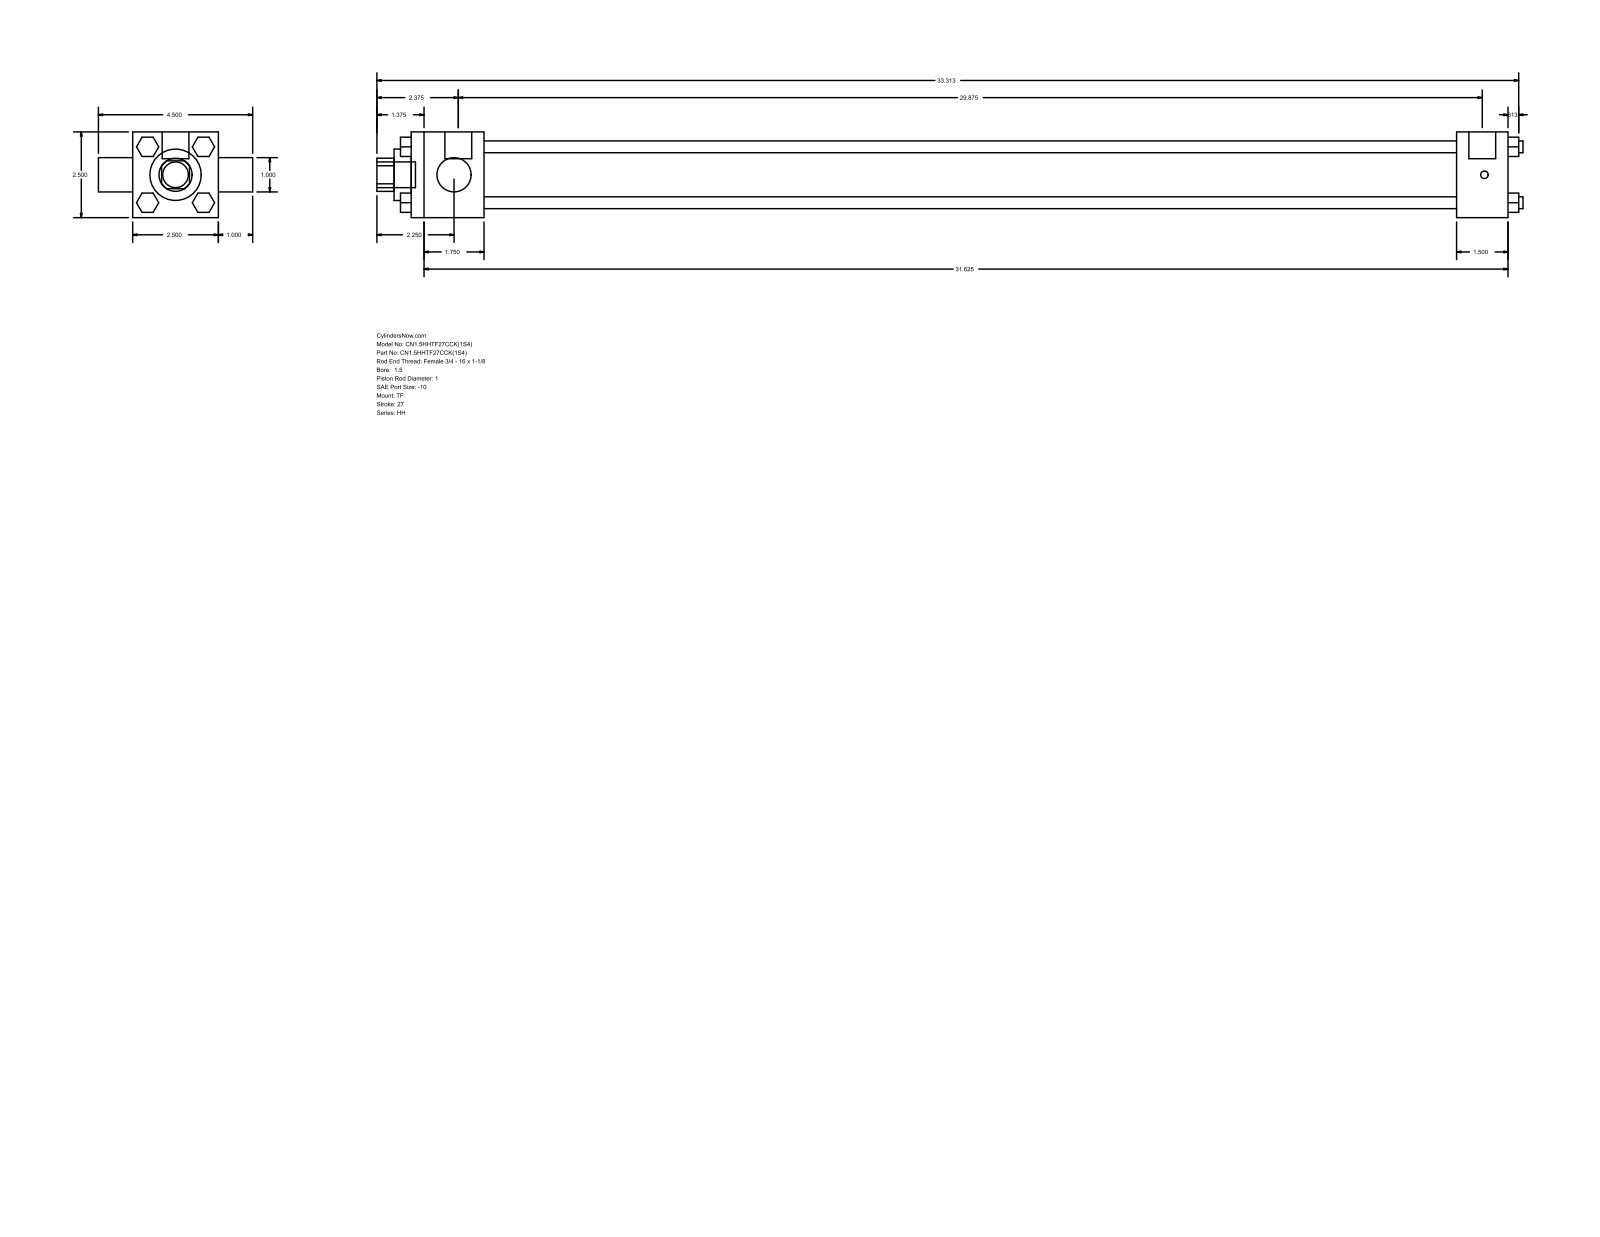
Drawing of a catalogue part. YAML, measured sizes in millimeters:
part_name: "HH_TF__0150_1"
step_written_by: "GSSL Pune (CONFIG_CONTROL_DESIGN)"
units: millimeters
bodies: {solids: 0, faces: 120, planar: 92, cylindrical: 28, other: 0}
overall_size: [849.31, 114.3, 63.5]
round_holes:
  - {diameter: 25.4, count: 2}
  - {diameter: 38.1, count: 1}
  - {diameter: 44.45, count: 1}
round_bosses_or_shafts:
  - {diameter: 8.76, count: 4}
  - {diameter: 5.56, count: 3}
  - {diameter: 19.84, count: 2}
  - {diameter: 19.05, count: 1}
partial_cylinders:
  - {radius: 12.29, count: 1}
face_to_face_distances: [63.5, 758.82, 720.72, 38.1, 53.98, 774.7, 812.8, 820.74, 25.4, 20.7]
